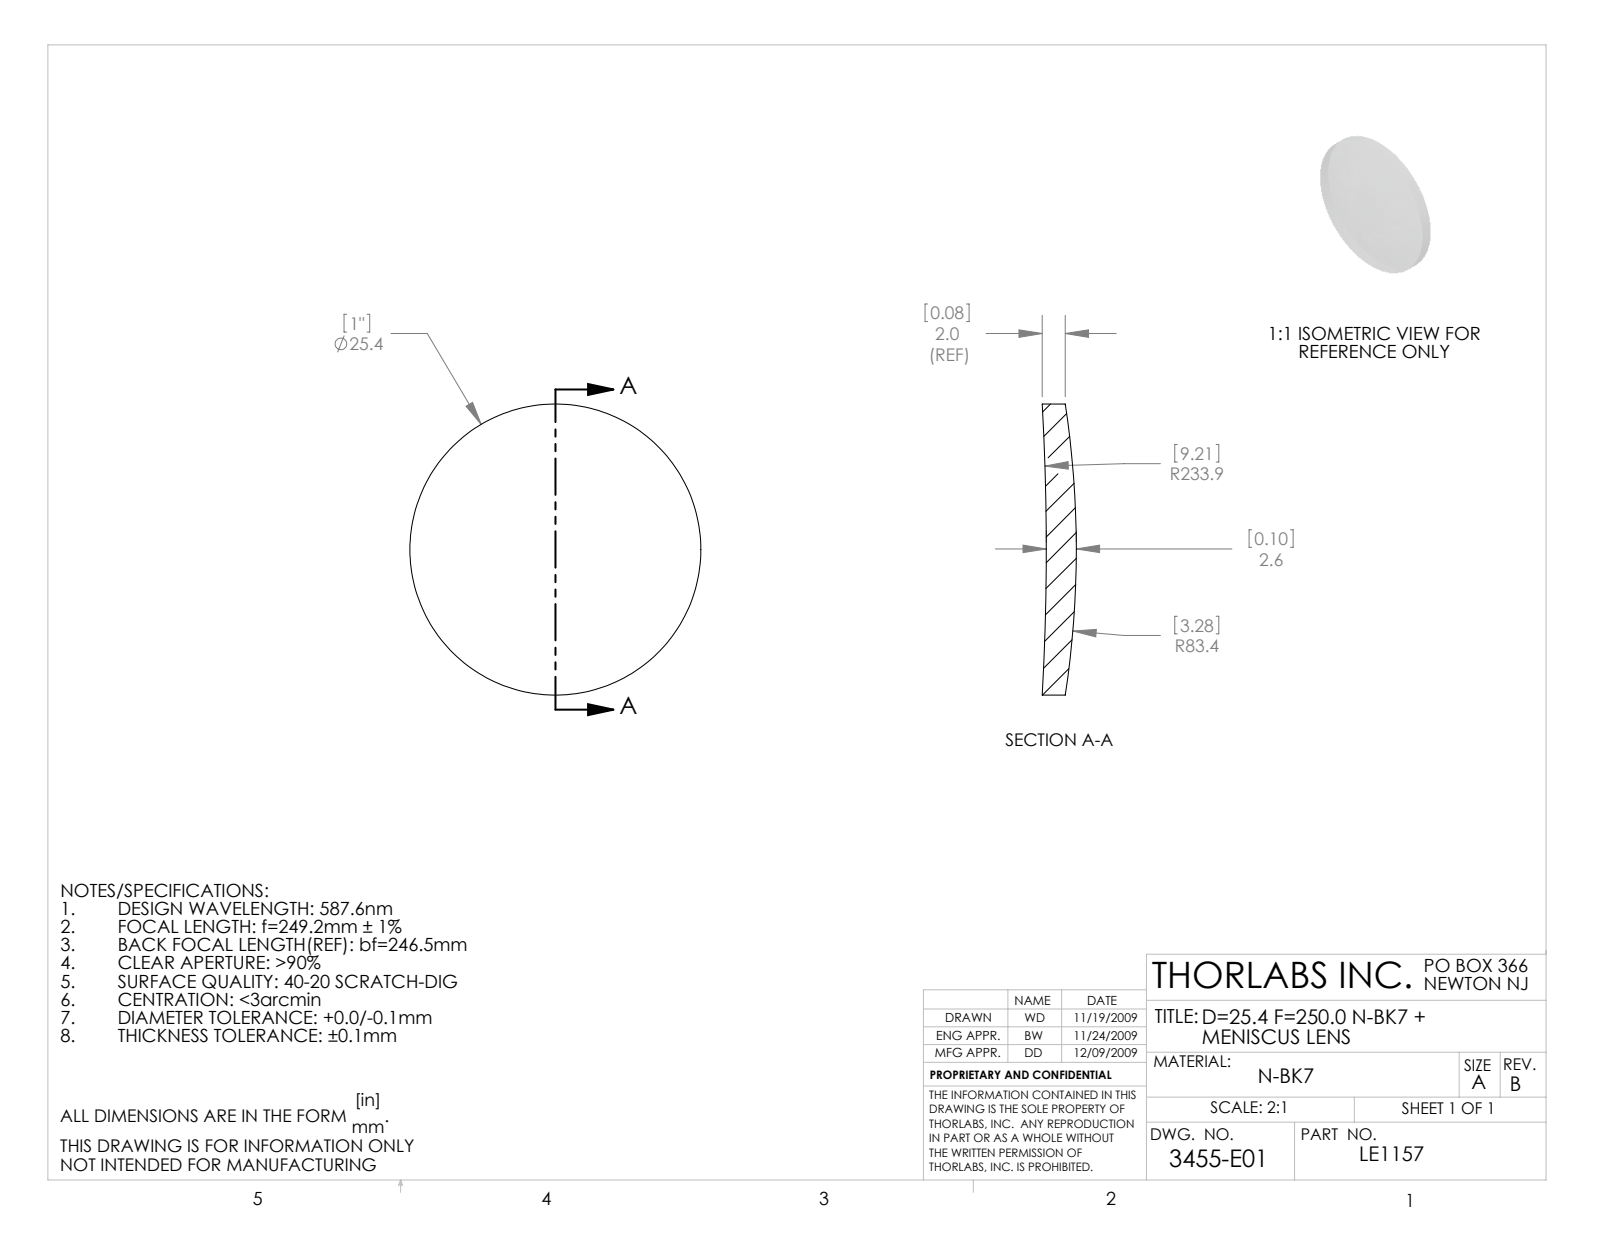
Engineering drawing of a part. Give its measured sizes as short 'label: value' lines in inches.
name: 3455-E0W
written by: SolidWorks 2009 (AUTOMOTIVE_DESIGN)
unit: in
bodies: 1 solid, 6 faces (0 planar, 2 cylindrical, 4 other)
size: 1 × 1 × 0.117
volume: 0.072 in³; area: 1.824 in²
bosses: 1× ⌀1
